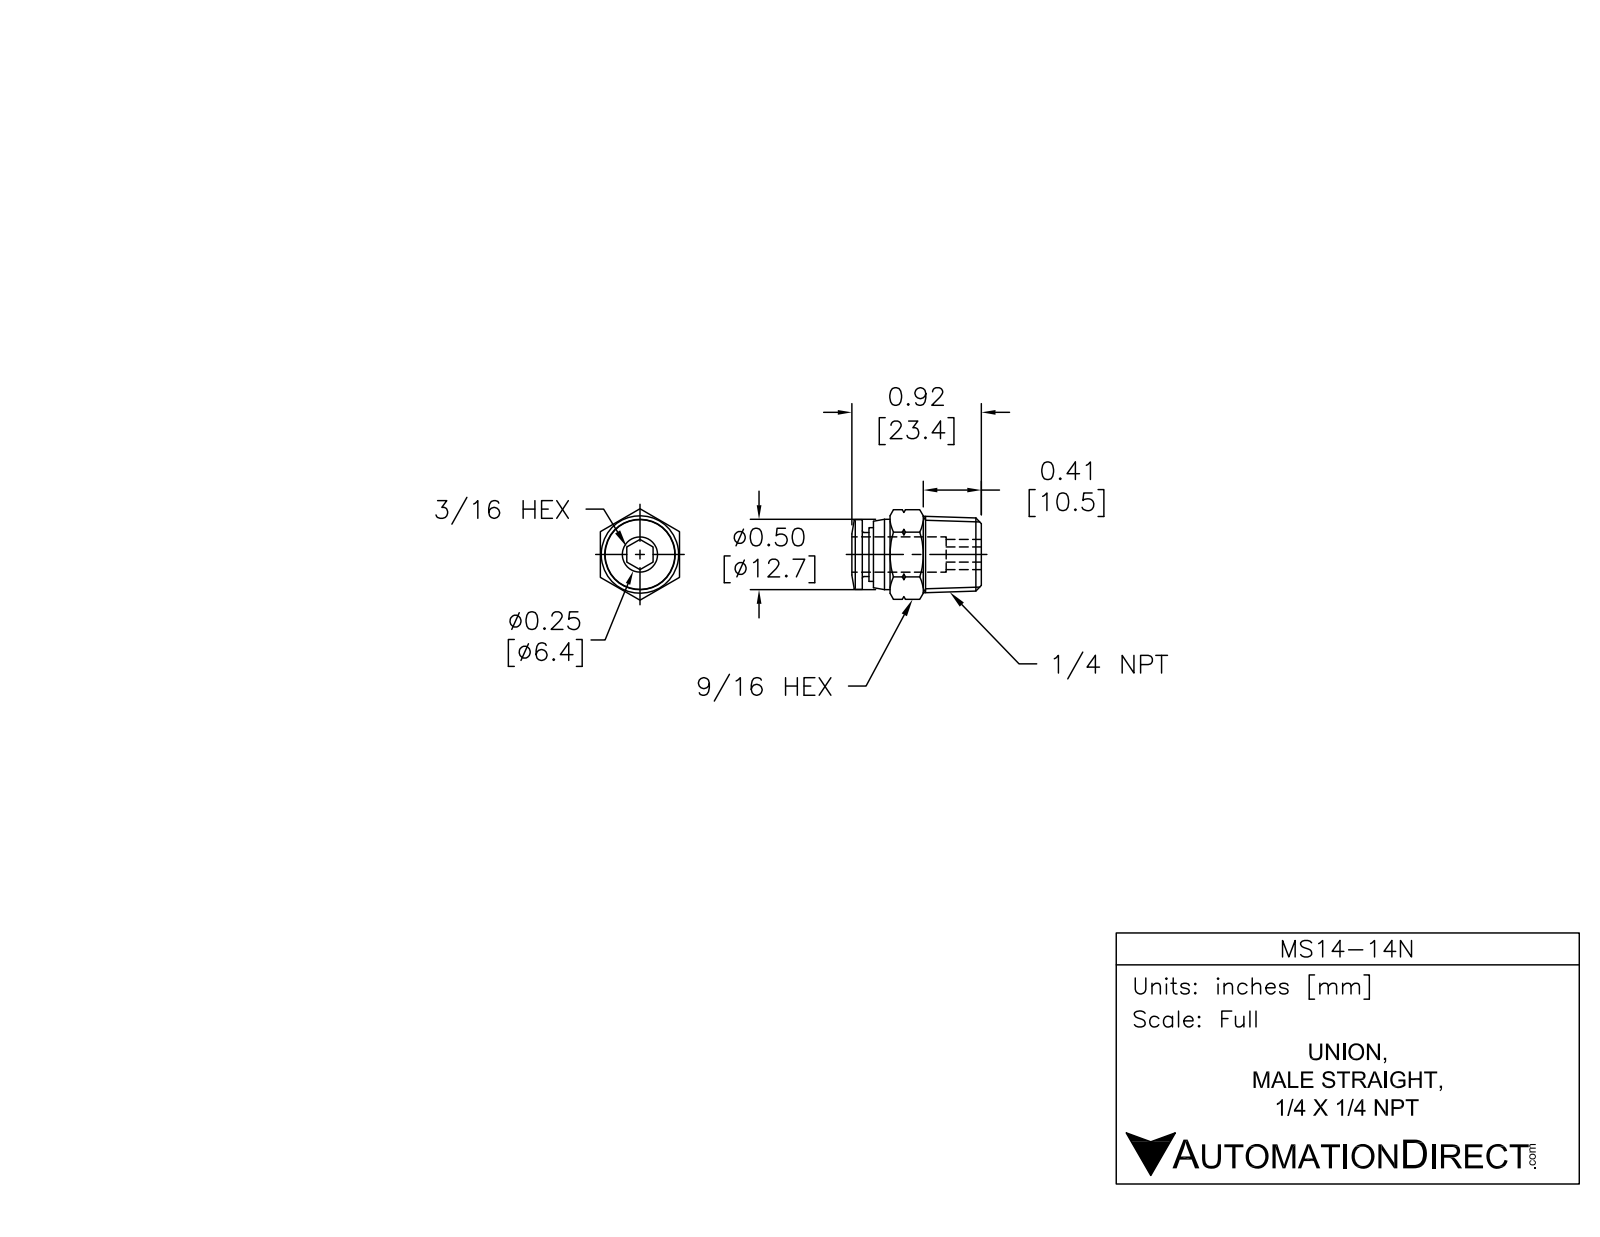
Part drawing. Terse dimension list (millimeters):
name: PC1-4--N02
written by: Autodesk Inventor 2008 (AUTOMOTIVE_DESIGN)
unit: mm
bodies: 1 solid, 51 faces (13 planar, 6 cylindrical, 32 other)
size: 23.4 × 16.17 × 14
volume: 2 502 mm³; area: 1 791 mm²
holes: 1× ⌀4.8, 1× ⌀6.55
bosses: 1× ⌀12.7, 1× ⌀12.6, 1× ⌀9.7, 1× ⌀7.95
face distances: 14, 21.5, 19.5, 2, 16.5, 3, 5, 20.3, 3.8, 0.8
